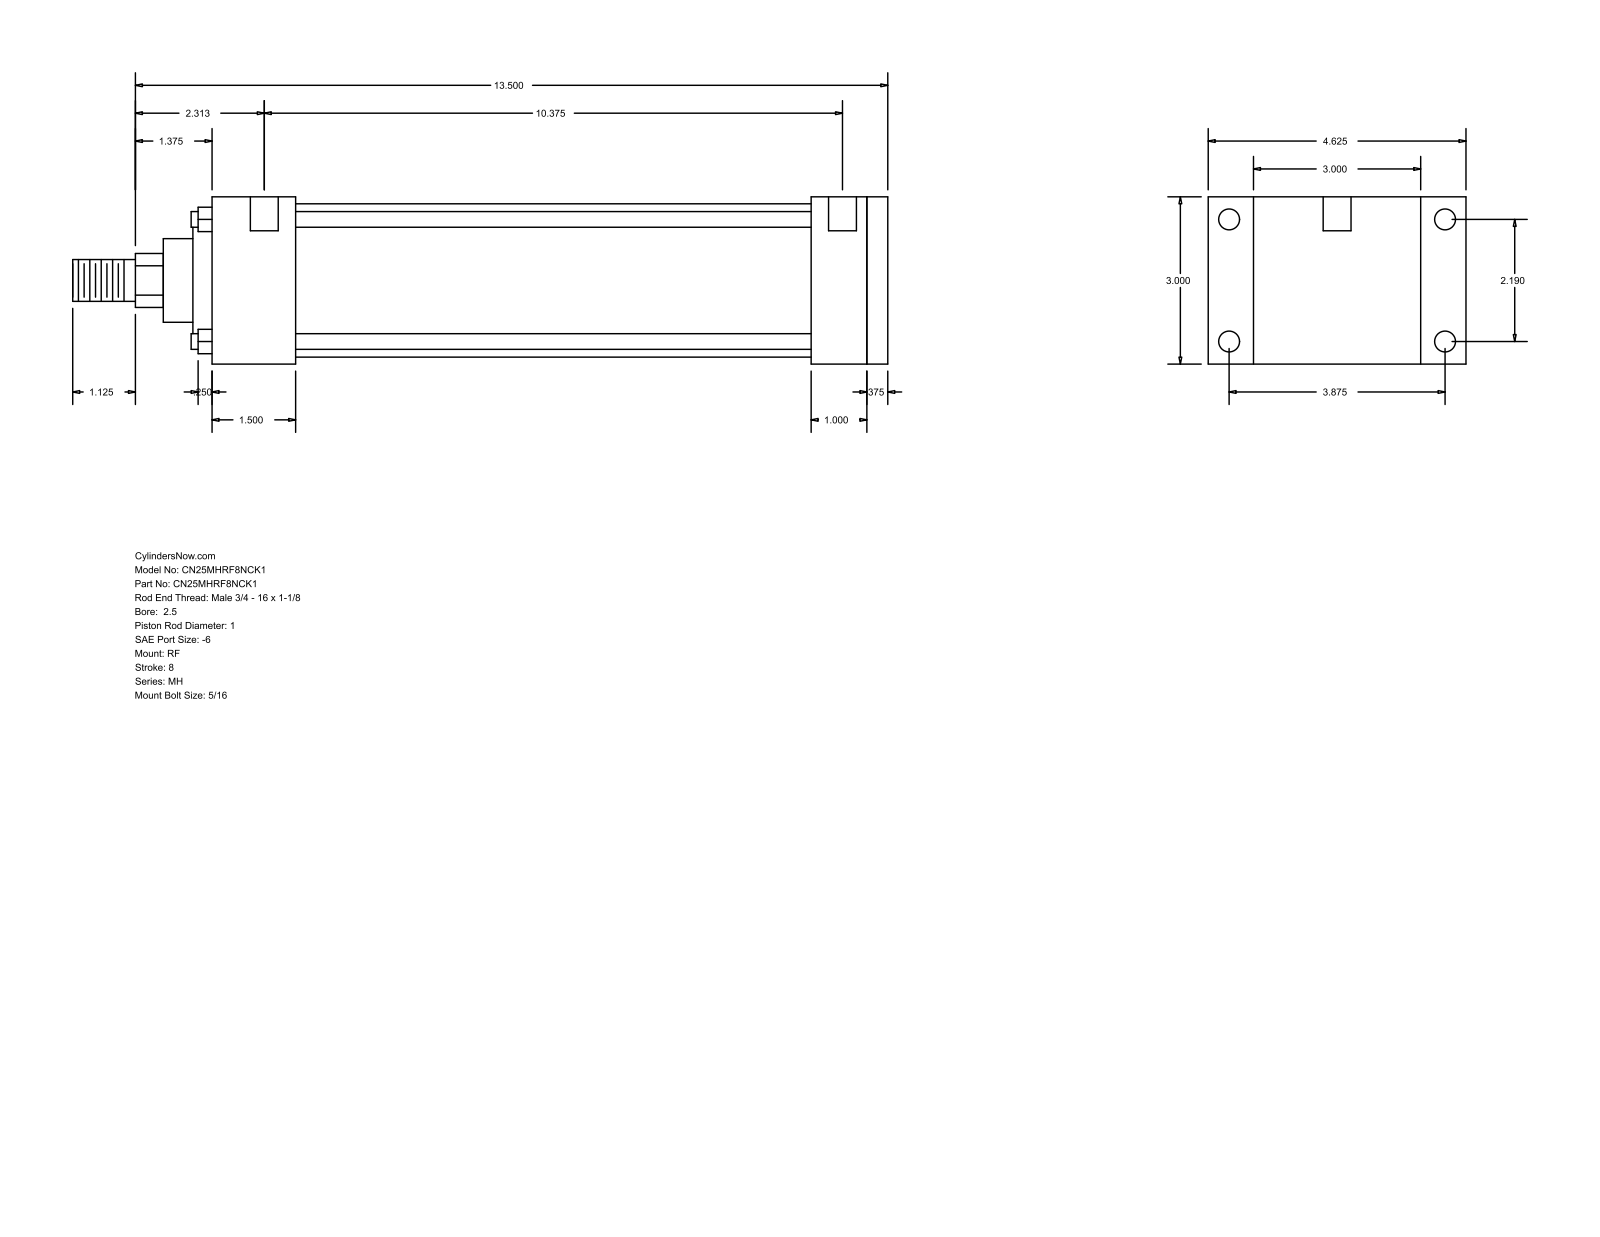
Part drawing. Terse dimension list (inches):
name: MH_RF__0250_1
written by: GSSL Pune (CONFIG_CONTROL_DESIGN)
unit: in
bodies: 0 solids, 94 faces (65 planar, 29 cylindrical, 0 other)
size: 14.625 × 4.625 × 3
holes: 4× ⌀0.219, 4× ⌀0.375, 2× ⌀0.5
bosses: 4× ⌀0.281, 1× ⌀2.75, 1× ⌀2.375, 1× ⌀1.5, 1× ⌀1, 1× ⌀0.75
rounds: 1× R0.484
face distances: 3, 0.375, 12.125, 11.75, 1, 1.375, 10.75, 1.5, 9.25, 10.25
hole spacings: 2.19, 3.875, 4.451, 10.687, 0.125, 0.187, 10.375, 10.5
